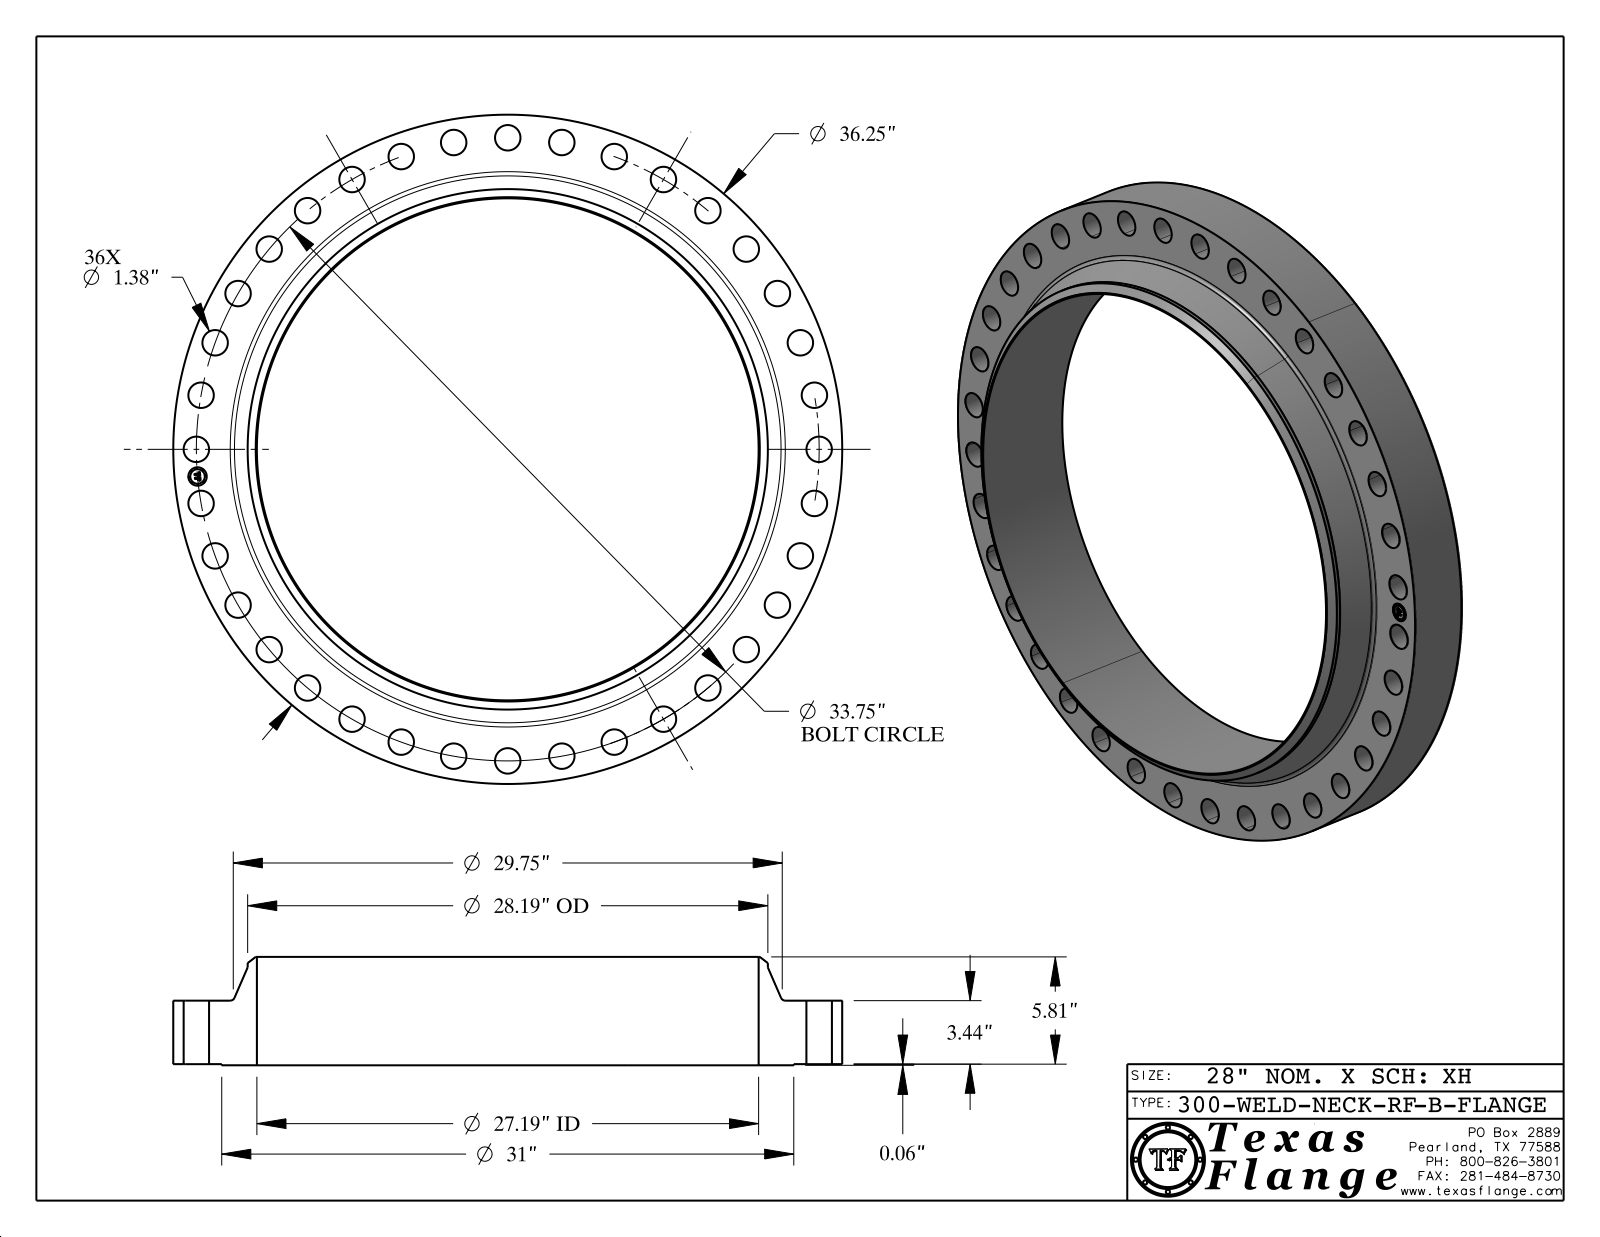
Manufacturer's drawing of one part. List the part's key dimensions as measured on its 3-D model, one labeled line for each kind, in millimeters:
Part name (STEP PRODUCT): 300-WELD-NECK-RF, Series B
STEP written by: CATIA V5 STEP AP214 (AUTOMOTIVE_DESIGN)
Units: millimetres
Bodies: 1 solid, 475 faces (369 planar, 100 cylindrical, 6 other)
Overall size (bounding box): 920.8 × 920.8 × 149.2
Volume: 25 220 000 mm³ · Surface area: 1 527 000 mm²
Round holes (diameter × count): ⌀35.1 ×36, ⌀25.4 ×1, ⌀690.6 ×1
Round bosses / shafts (diameter × count): ⌀1.5 ×8, ⌀920.8 ×1, ⌀787.4 ×1, ⌀716 ×1, ⌀20 ×1
Main face-to-face distances: 87.4, 1.6, 89, 149.2, 147.6, 60.2, 0.4, 88.6, 87, 60.6
Hole centre spacings: 428.6, 854, 828, 428.6, 606.2, 74.7, 551, 656.7
